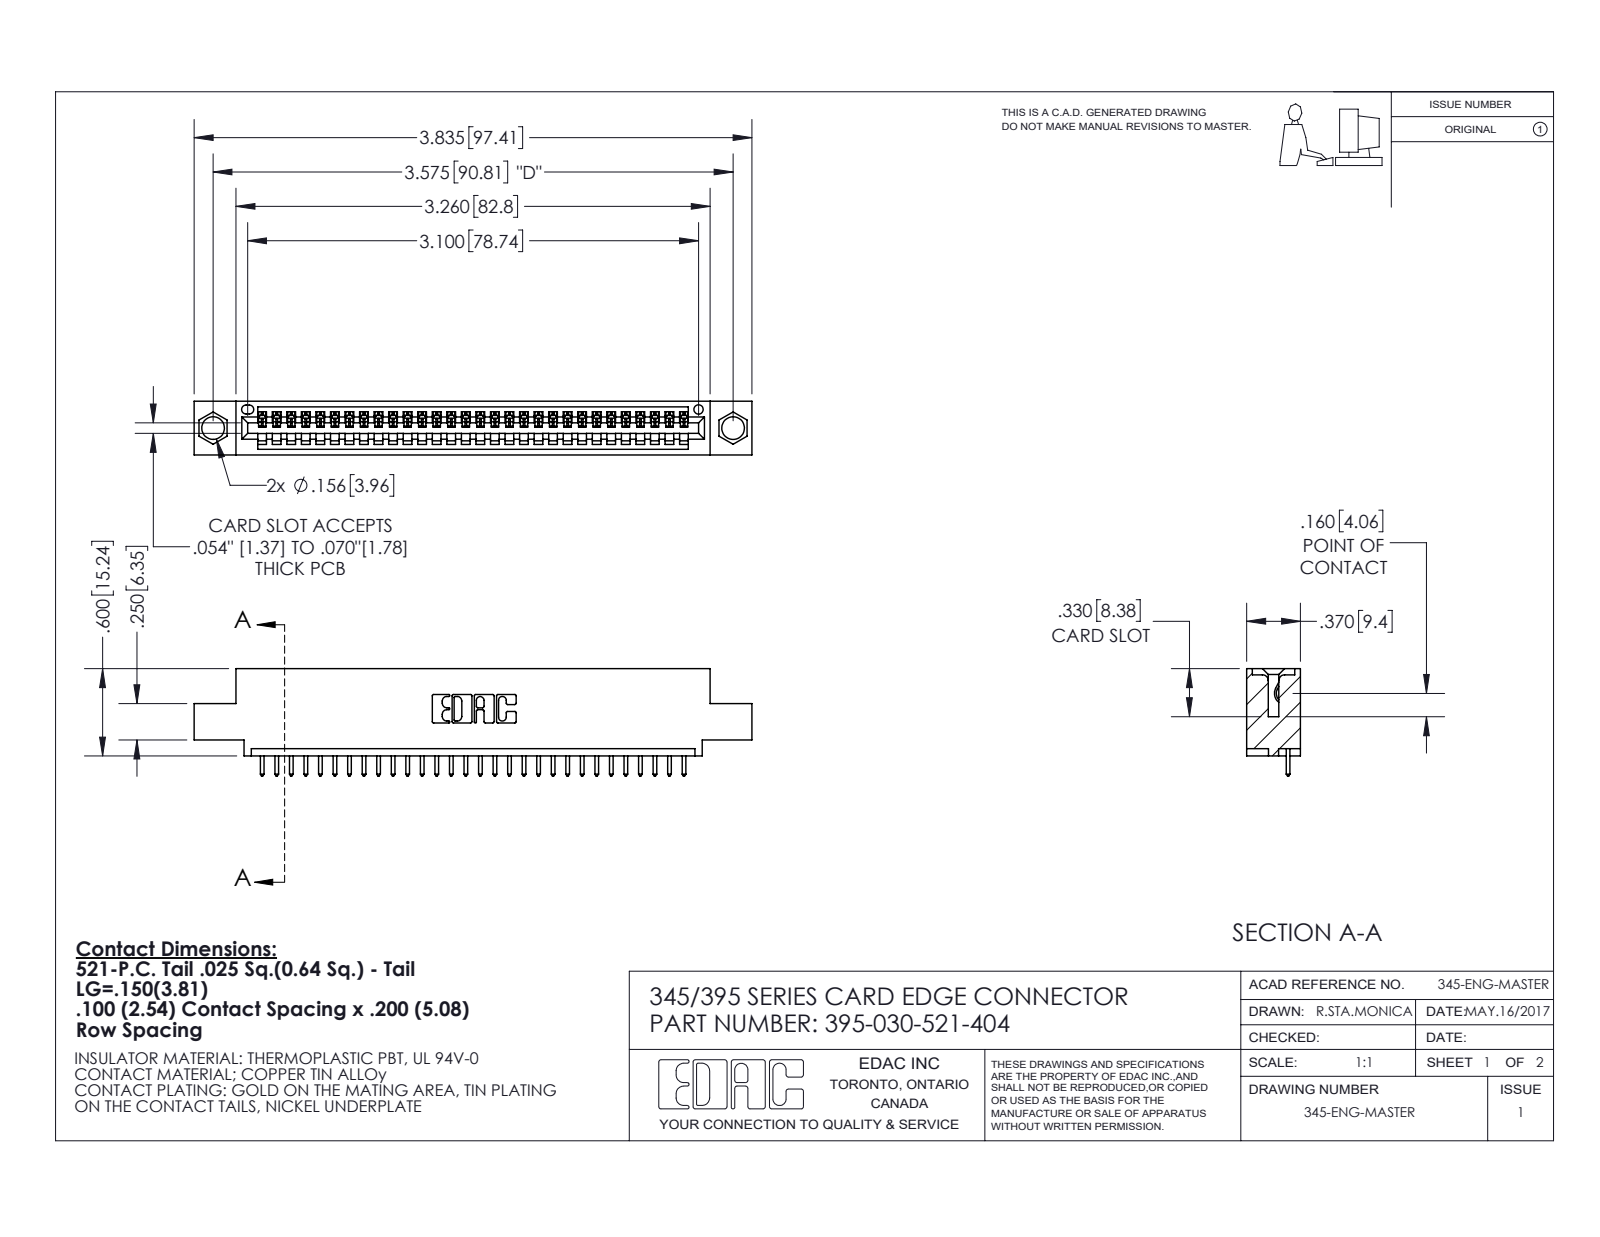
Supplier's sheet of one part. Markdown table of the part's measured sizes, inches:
| quantity | value |
| --- | --- |
| part name | 395-030-521-404; 345 Part_0.110 Offset - 0.156 Dia-TI; 345-292-001_345-293-121 |
| STEP written by | SolidWorks 2020 (CONFIG_CONTROL_DESIGN) |
| units | inches |
| bodies | 31 solids, 1884 faces (1298 planar, 586 cylindrical, 0 other) |
| overall size | 3.835 × 0.737 × 0.37 |
| volume | 0.542 in³ |
| surface area | 17.42 in² |
| round holes (diameter × count) | 0.156 × 2, 0.064 × 1 |
| partial cylindrical surfaces (radius × count) | 0.006 × 60, 0.01 × 60, 0.01 × 22, 0.007 × 6, 0.031 × 6, 0.026 × 3, 0.031 × 2, 0.04 × 2 |
| main face-to-face distances | 0.298, 0.072, 0.37, 0.2, 0.098, 0.272, 0.025, 0.225, 0.149, 0.072 |
| hole center spacings | 0.27, 3.34, 3.575 |
